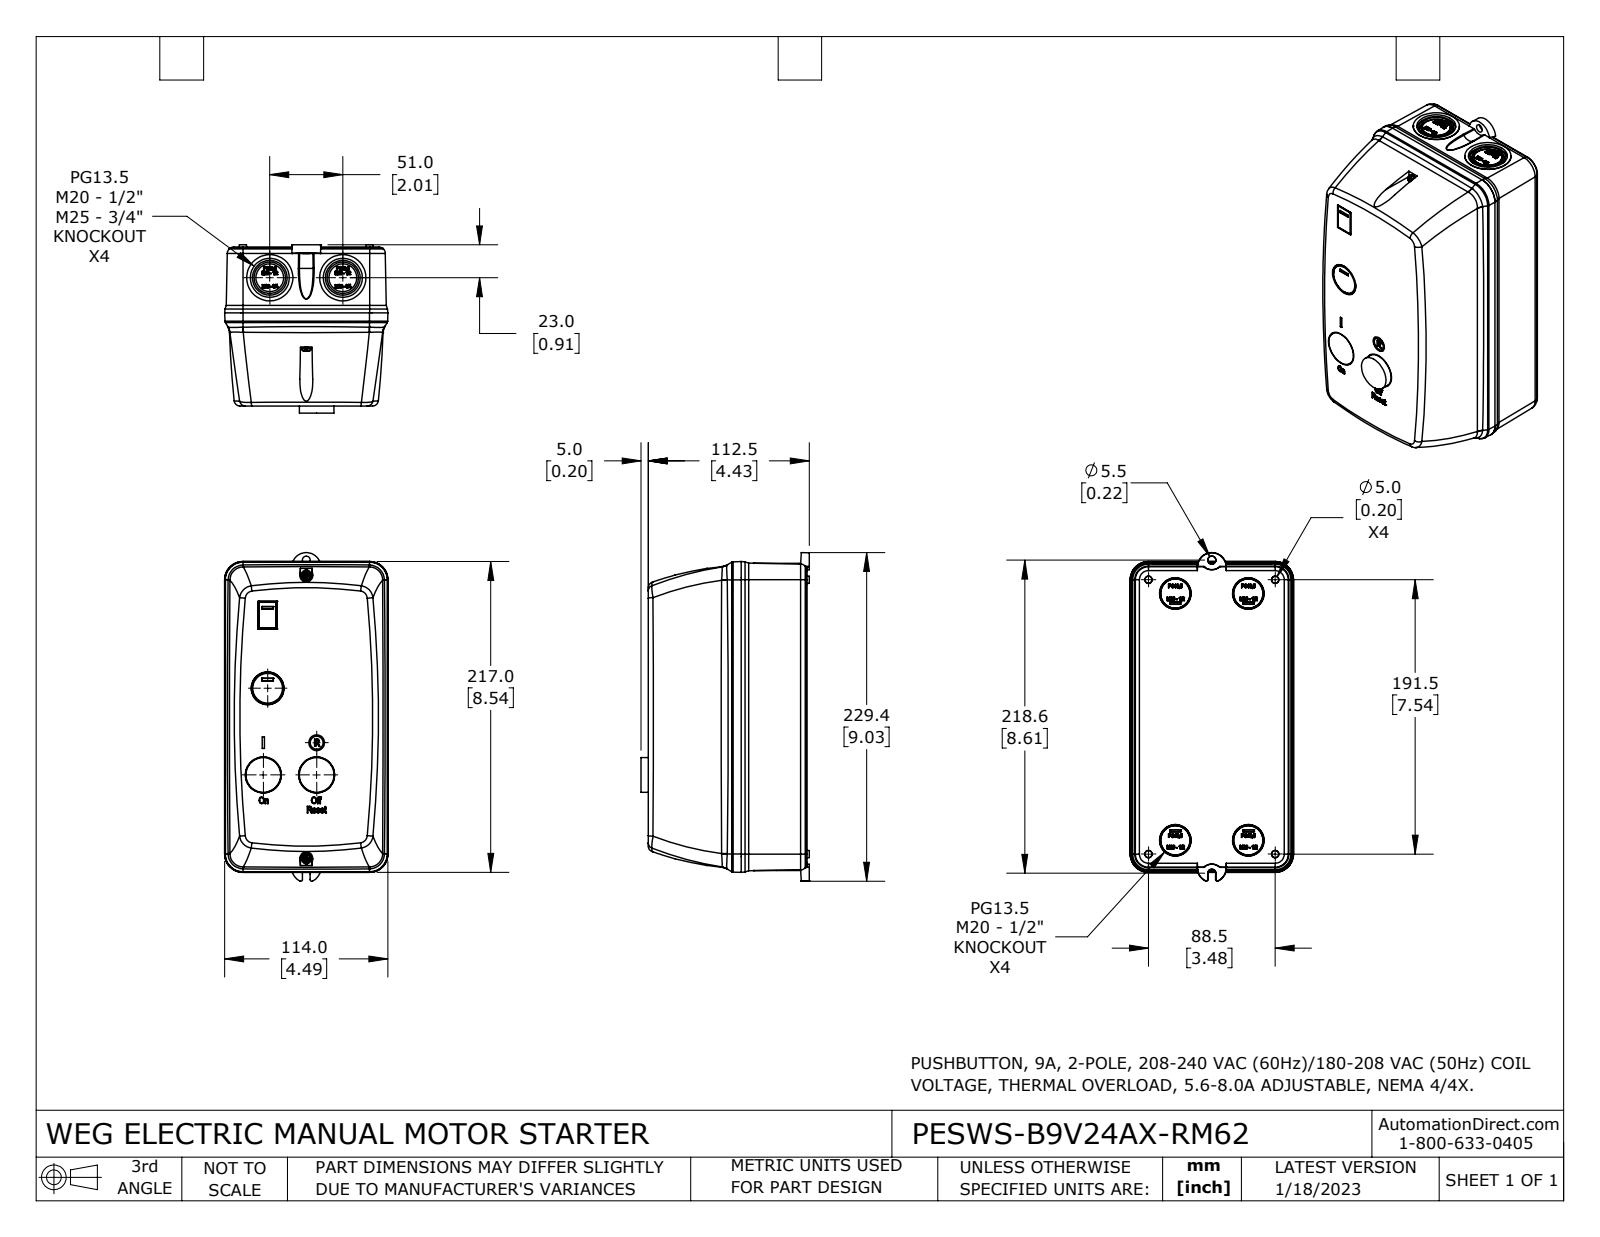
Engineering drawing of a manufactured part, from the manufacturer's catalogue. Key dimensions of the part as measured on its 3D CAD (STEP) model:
Part name (STEP PRODUCT): PESWS-B9V24AX-RM62
STEP written by: SolidWorks 2021 (CONFIG_CONTROL_DESIGN)
Units: millimetres
Bodies: 6 solids, 2195 faces (1110 planar, 92 cylindrical, 993 other)
Overall size (bounding box): 229.44 × 117.5 × 114.01
Volume: 2 457 000 mm³ · Surface area: 166 196 mm²
Round holes (diameter × count): ⌀4.4 ×2, ⌀21.91 ×2, ⌀27.24 ×2, ⌀5.5 ×1, ⌀11 ×1
Round bosses / shafts (diameter × count): ⌀32.26 ×2, ⌀24.25 ×2, ⌀24.2 ×2, ⌀19.37 ×2, ⌀7 ×2, ⌀3 ×2, ⌀9 ×1
Partial cylindrical surfaces — rounded edges, fillets, slot ends (radius × count): R2 ×4, R4.61 ×4, R9.54 ×4, R6.54 ×2, R7.54 ×2, R2.08 ×1, R2.17 ×1, R2.75 ×1
Main face-to-face distances: 46, 65, 111, 0.5, 110.5, 45.5, 110, 1, 109.5, 64
Hole centre spacings: 10.5, 51, 81.32, 117.22, 127.71, 198, 208.5
